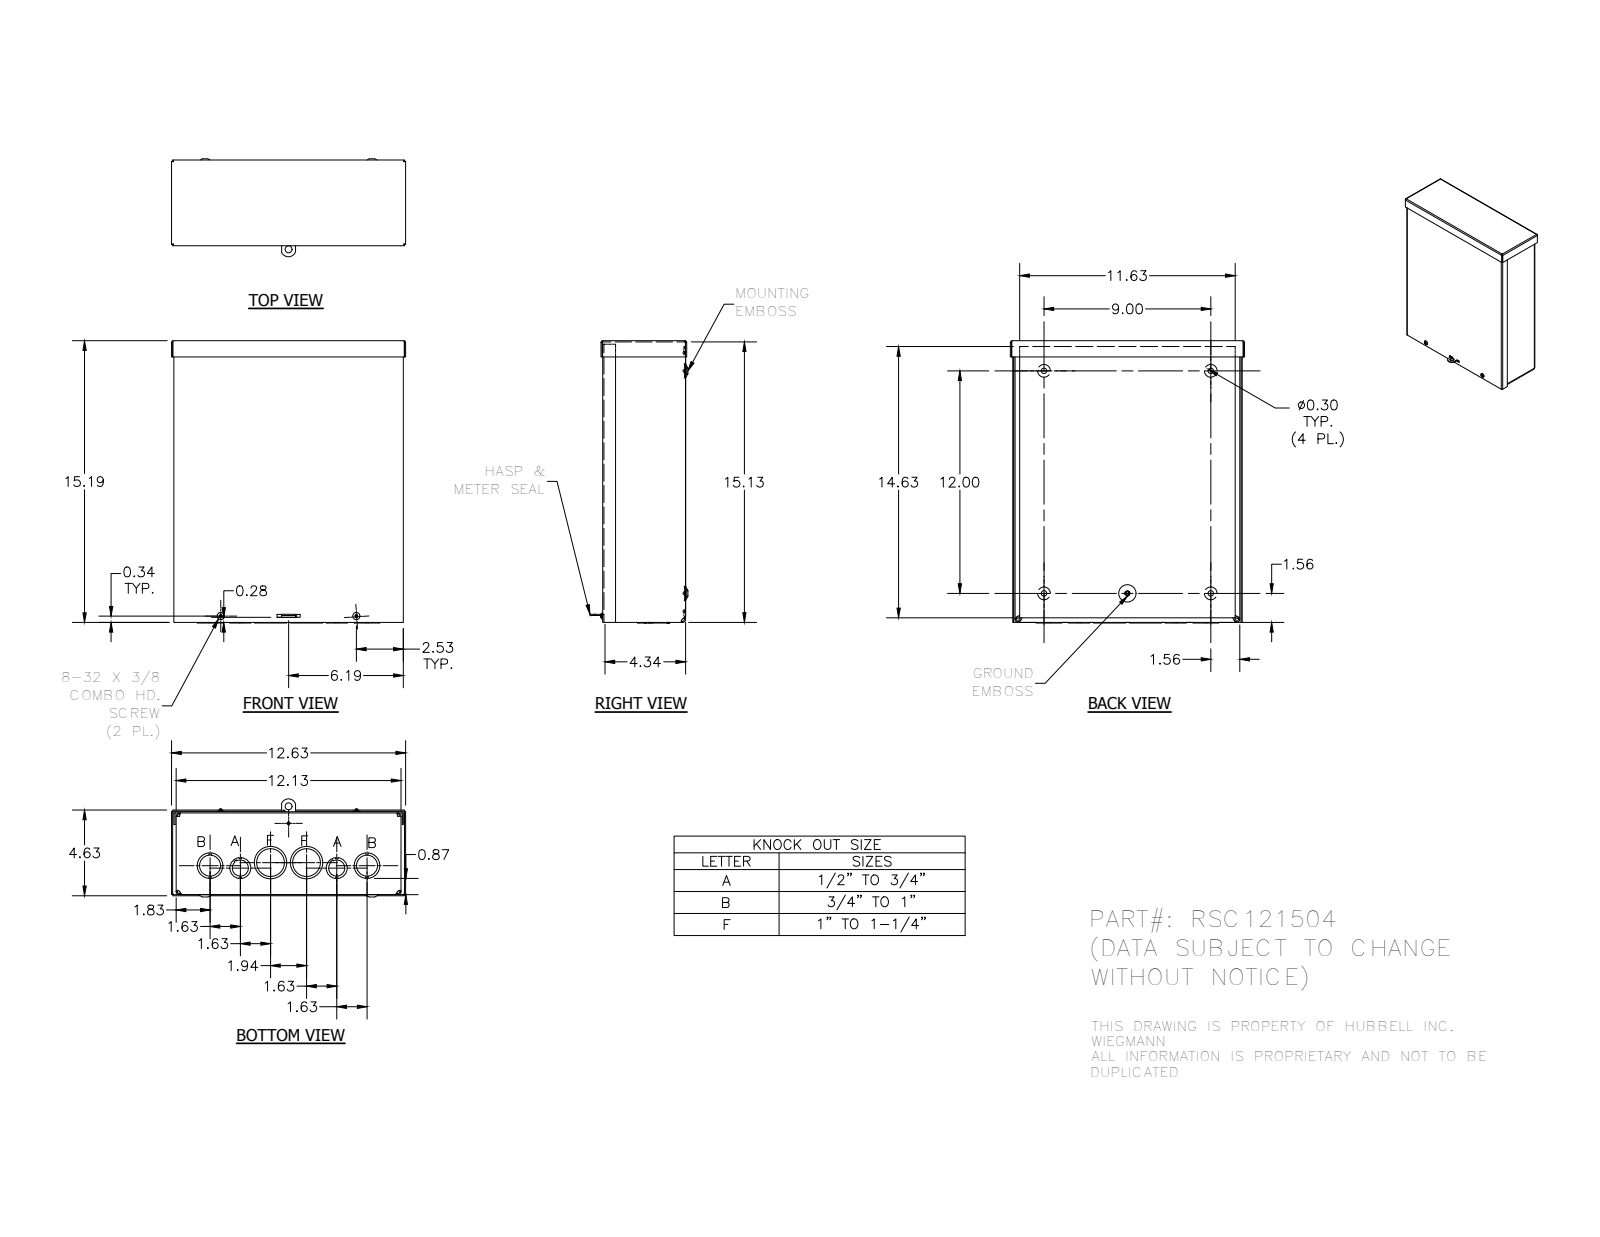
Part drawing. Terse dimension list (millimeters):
name: RSC121504; RSC121504_WRAP; RSC1215_LID; RSC1204_CAP (+4 more)
written by: Autodesk Inventor 2012 (AUTOMOTIVE_DESIGN)
unit: mm
bodies: 7 solids, 551 faces (264 planar, 143 cylindrical, 144 other)
size: 388.1 × 320.7 × 130.2
volume: 776 100 mm³; area: 998 100 mm²
holes: 4× ⌀7.6, 4× ⌀8, 4× ⌀28.6, 2× ⌀3.2, 2× ⌀3.8, 2× ⌀22.2, 2× ⌀34.9, 2× ⌀38.1, 2× ⌀44.5, 1× ⌀4, 1× ⌀4.2, 1× ⌀9.5
bosses: 2× ⌀9.8, 2× ⌀4.2, 1× ⌀5.8
rounds: 14× R0.3, 8× R0.8, 8× R2.4, 8× R3.2, 8× R4.7, 6× R0.8, 5× R0.6, 4× R1.4
face distances: 1.6, 107.9, 106.3, 1.6, 109.5, 108, 1.6, 308, 3.1, 384.2
hole spacings: 34.4, 41.5, 42.1, 77, 82.9, 91, 114.3, 132.2
